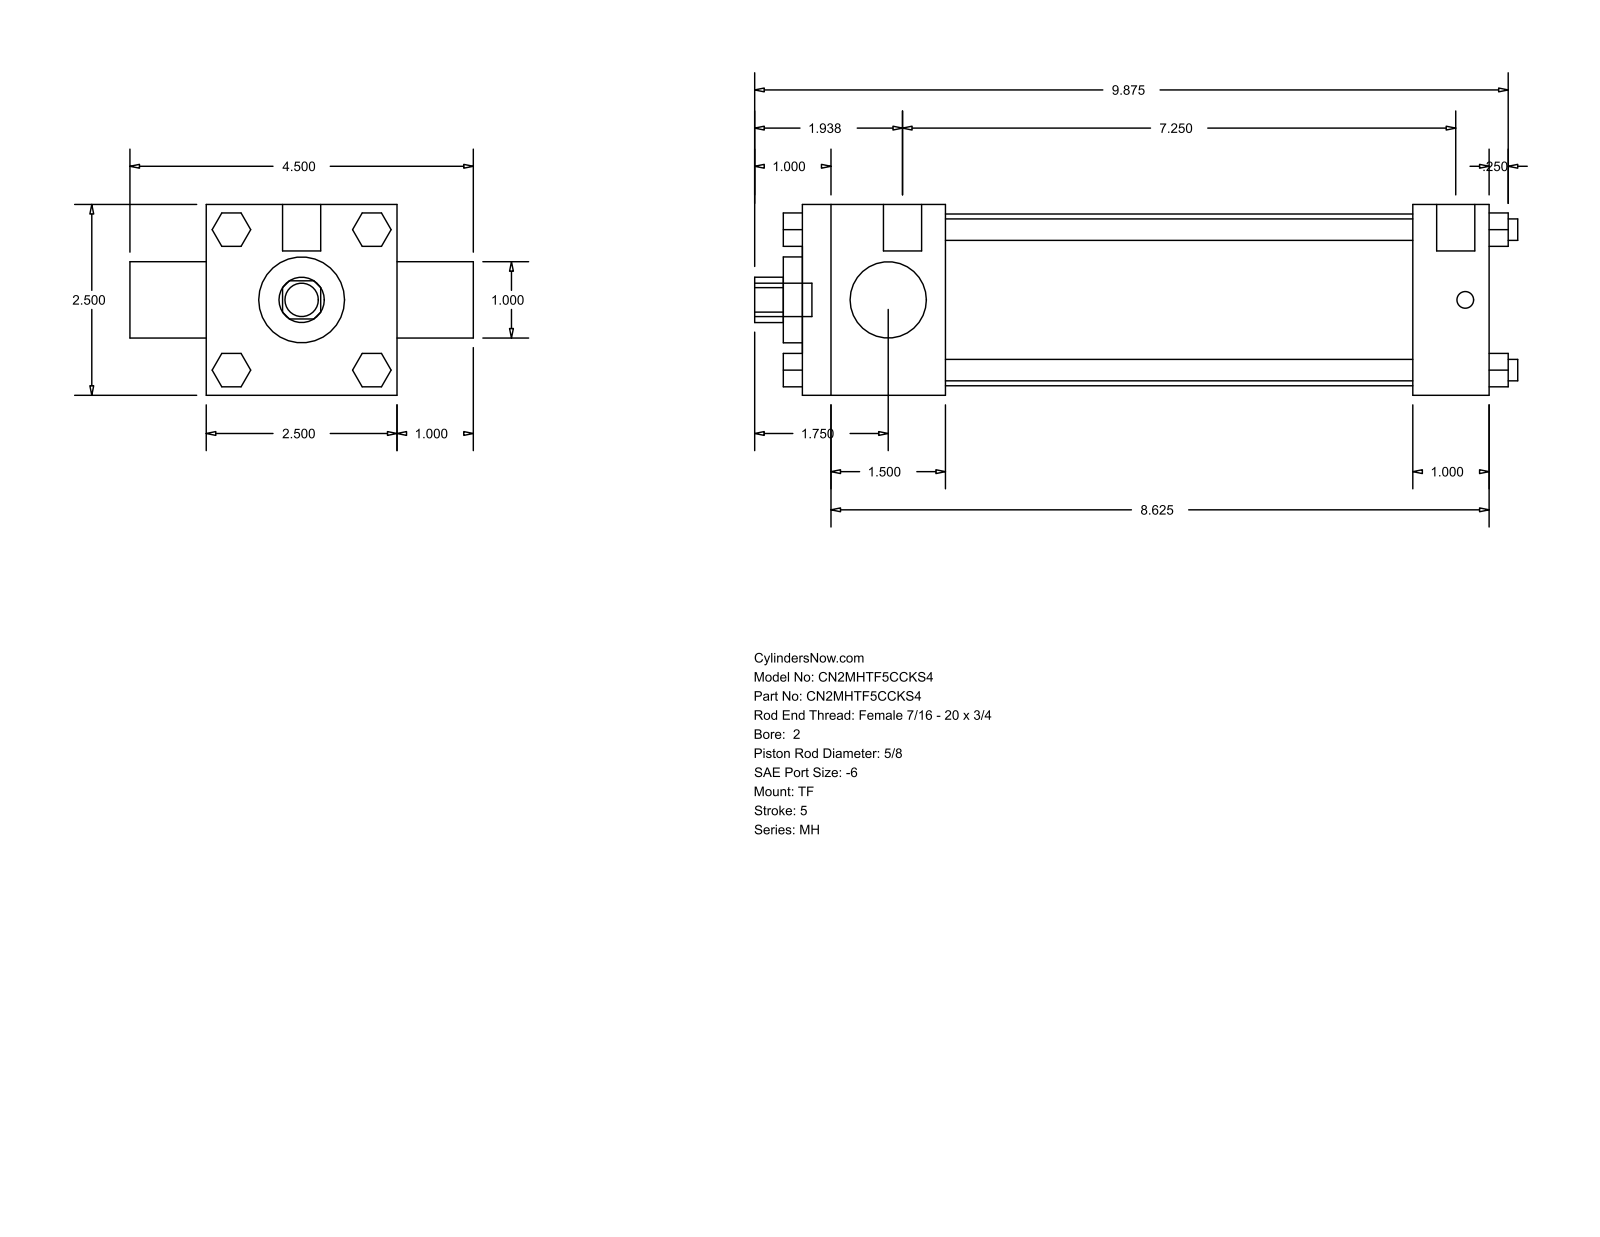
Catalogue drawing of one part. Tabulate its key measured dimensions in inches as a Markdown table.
| quantity | value |
| --- | --- |
| part name | MH_TF__0200_0.625 |
| STEP written by | GSSL Pune (CONFIG_CONTROL_DESIGN) |
| units | inches |
| bodies | 0 solids, 120 faces (92 planar, 28 cylindrical, 0 other) |
| overall size | 10 × 4.5 × 2.5 |
| round holes (diameter × count) | 0.625 × 1, 1 × 1, 1.125 × 1, 2.25 × 1 |
| round bosses / shafts (diameter × count) | 0.281 × 4, 0.219 × 3, 0.5 × 2, 0.437 × 1 |
| partial cylindrical surfaces (radius × count) | 0.297 × 1 |
| main face-to-face distances | 2.5, 9, 1, 1.875, 8, 6.125, 7.125, 0.25, 3.5, 9.25 |
